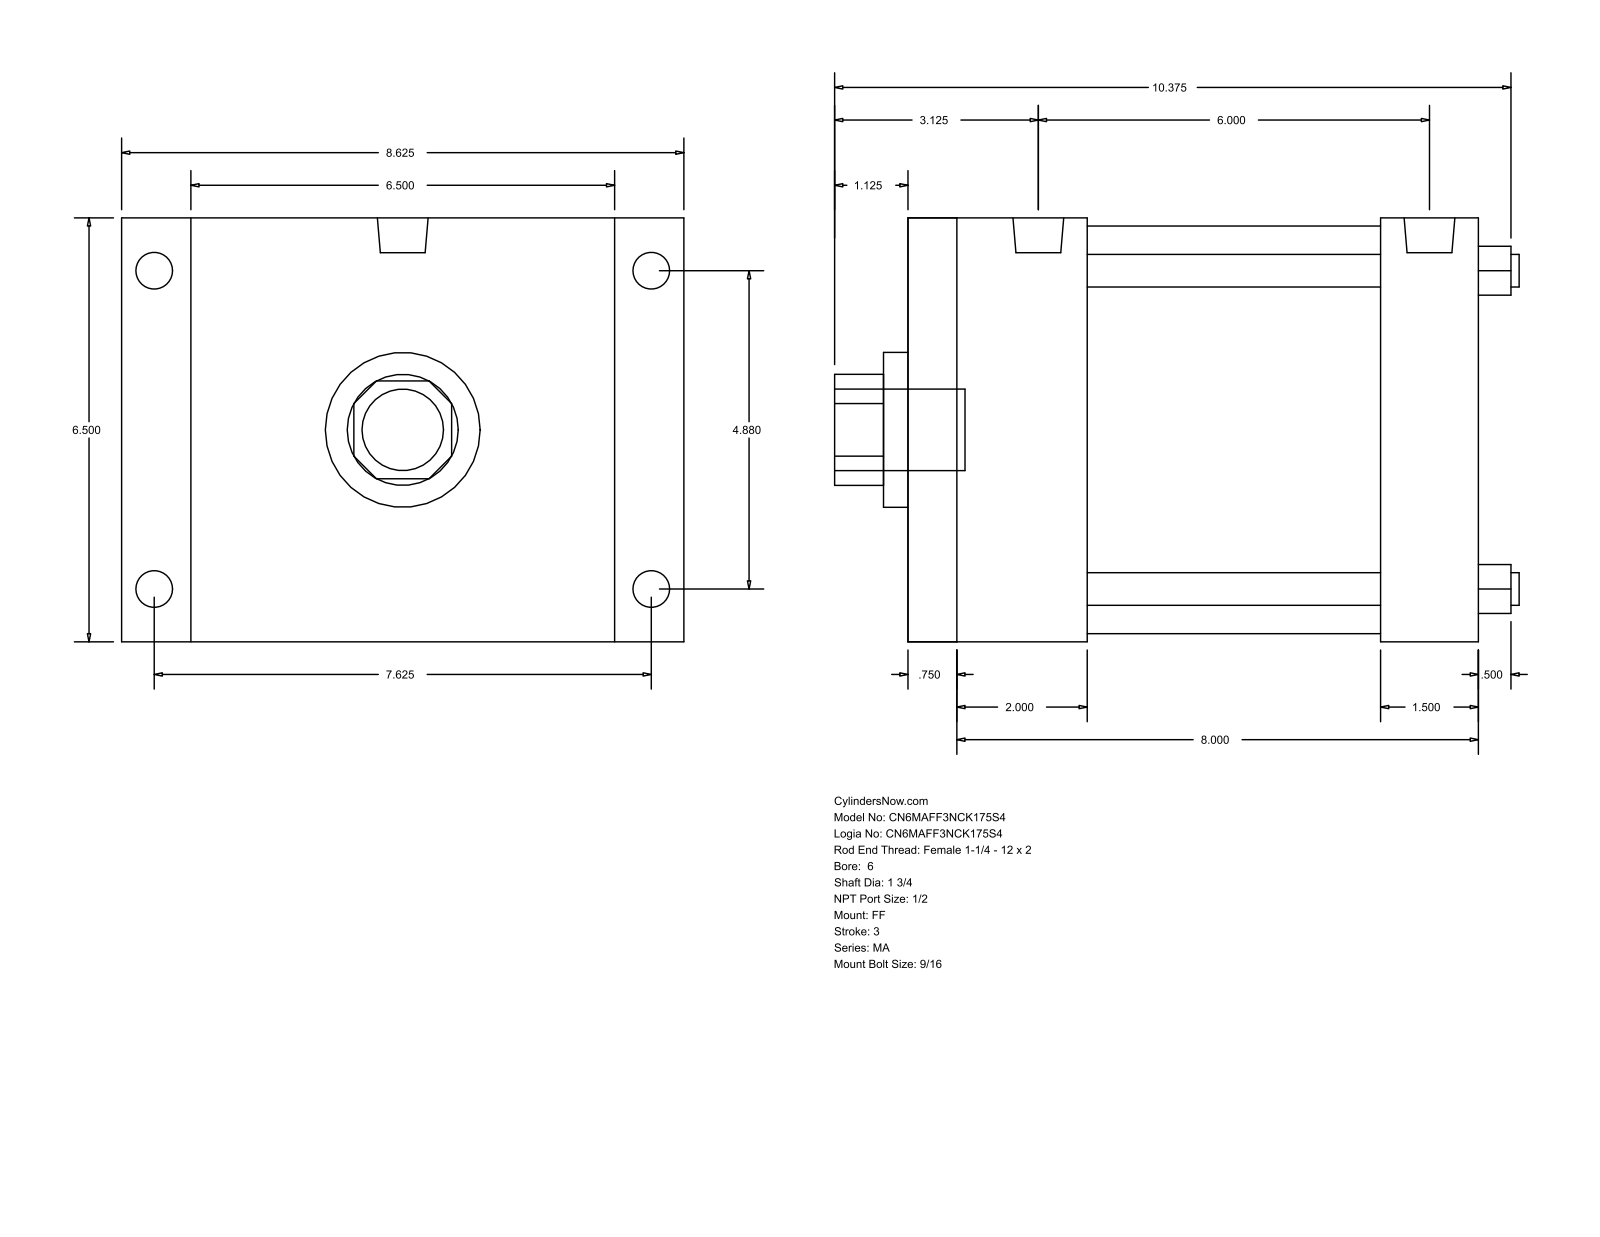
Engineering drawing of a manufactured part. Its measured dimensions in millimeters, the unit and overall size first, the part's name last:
Units: millimetres
Overall size (bounding box): 266.7 × 219.07 × 165.1
Round holes (diameter × count): ⌀12.7 ×4, ⌀44.45 ×1, ⌀60.33 ×1, ⌀158.75 ×1
Round bosses / shafts (diameter × count): ⌀17.46 ×4, ⌀14.29 ×4, ⌀19.77 ×2, ⌀31.75 ×1
Partial cylindrical surfaces — rounded edges, fillets, slot ends (radius × count): R21.63 ×1
Main face-to-face distances: 165.1, 222.25, 19.05, 203.2, 50.8, 38.1, 69.85, 152.4, 184.15, 114.3
Hole centre spacings: 87.65, 123.96, 175.31
Bodies: 0 solids, 92 faces (64 planar, 28 cylindrical, 0 other)
Part name (STEP PRODUCT): MA_FF__0600_1.75
STEP written by: GSSL Pune (CONFIG_CONTROL_DESIGN)
